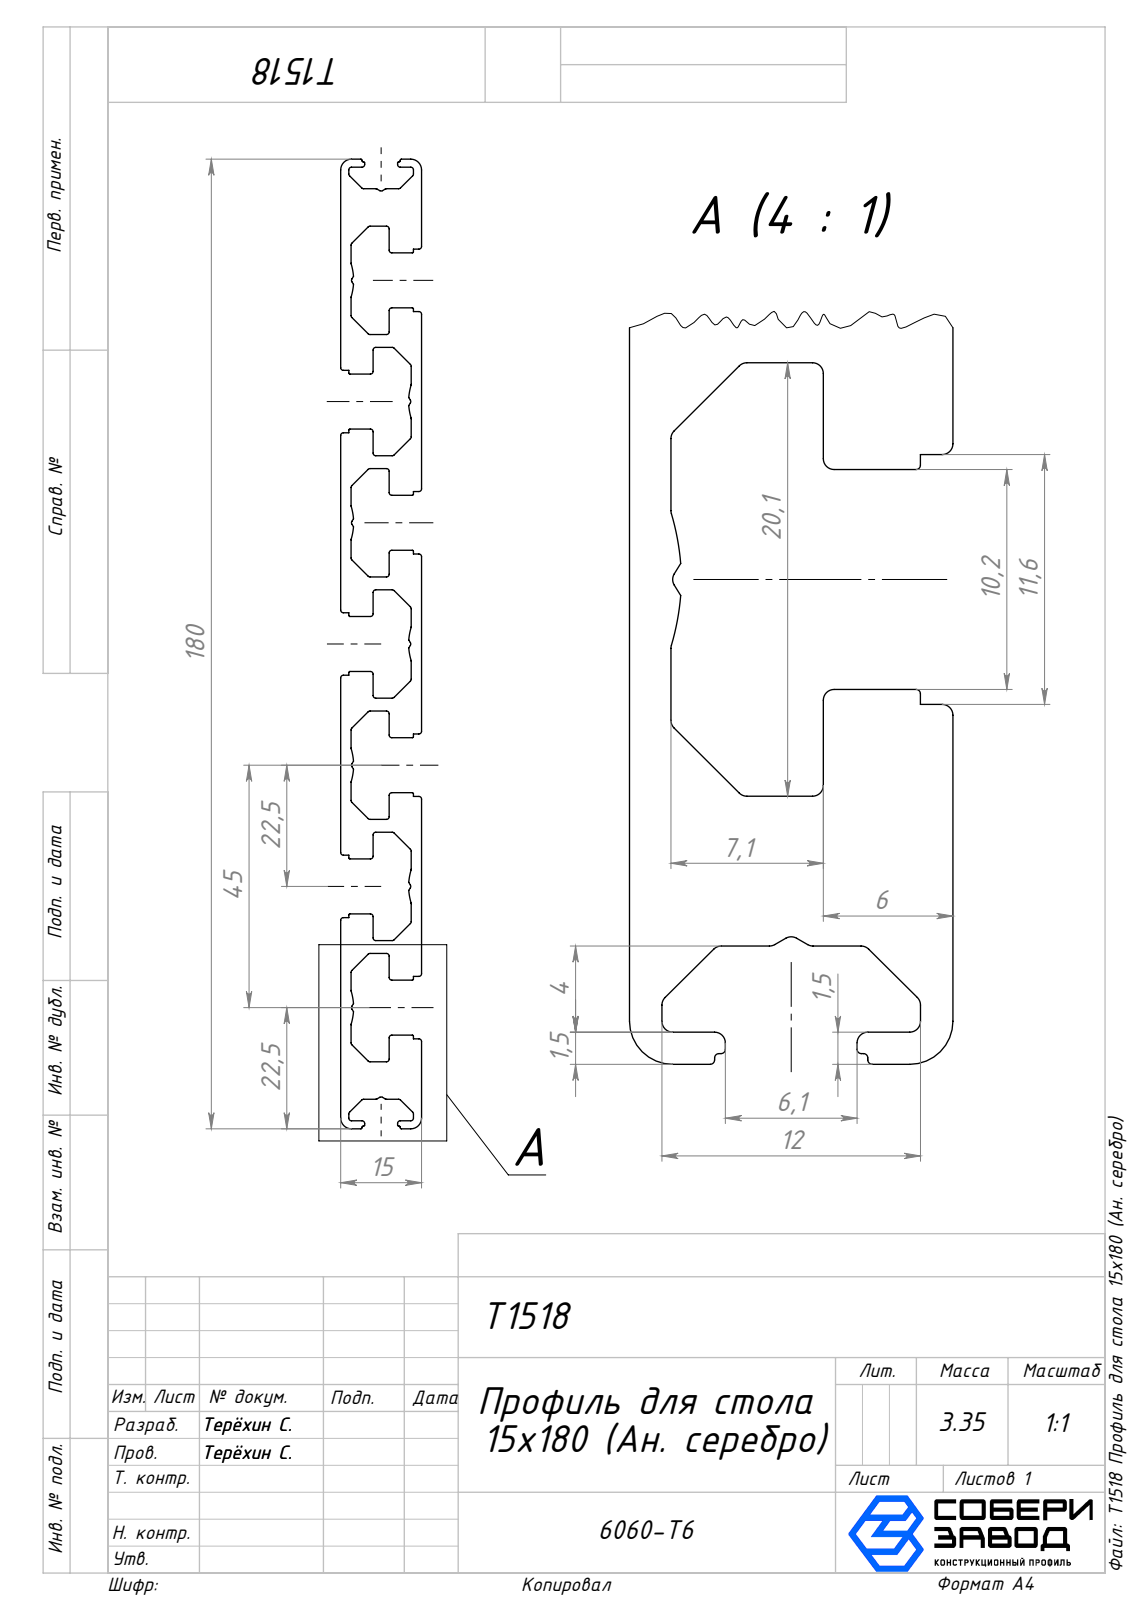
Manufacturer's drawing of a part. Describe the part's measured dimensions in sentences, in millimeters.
The part is named "T1518 Профиль для стола 15х180 (Ан. серебро); T1518 Профиль для стола 15х180 (Ан. серебро)_00". Its 3-D file was written by "SolidWorks 2025 (CONFIG_CONTROL_DESIGN)". It is 1 solid with 317 faces: 159 planar, 154 cylindrical and 4 other. Overall it measures 1000 by 180 by 15 millimeters. Its volume is 1 242 000 cubic millimeters and its surface area 711 924 square millimeters. Partial cylindrical surfaces (rounded edges, fillets, slot ends): 113 of radius 0.5, 22 of radius 0.2, 14 of radius 11.51, 4 of radius 2. The main face-to-face distances are 15, 6.01, 8.99, 1.92, 13.08, 7.07, 22.5, 4.09, 31.86, 45.
